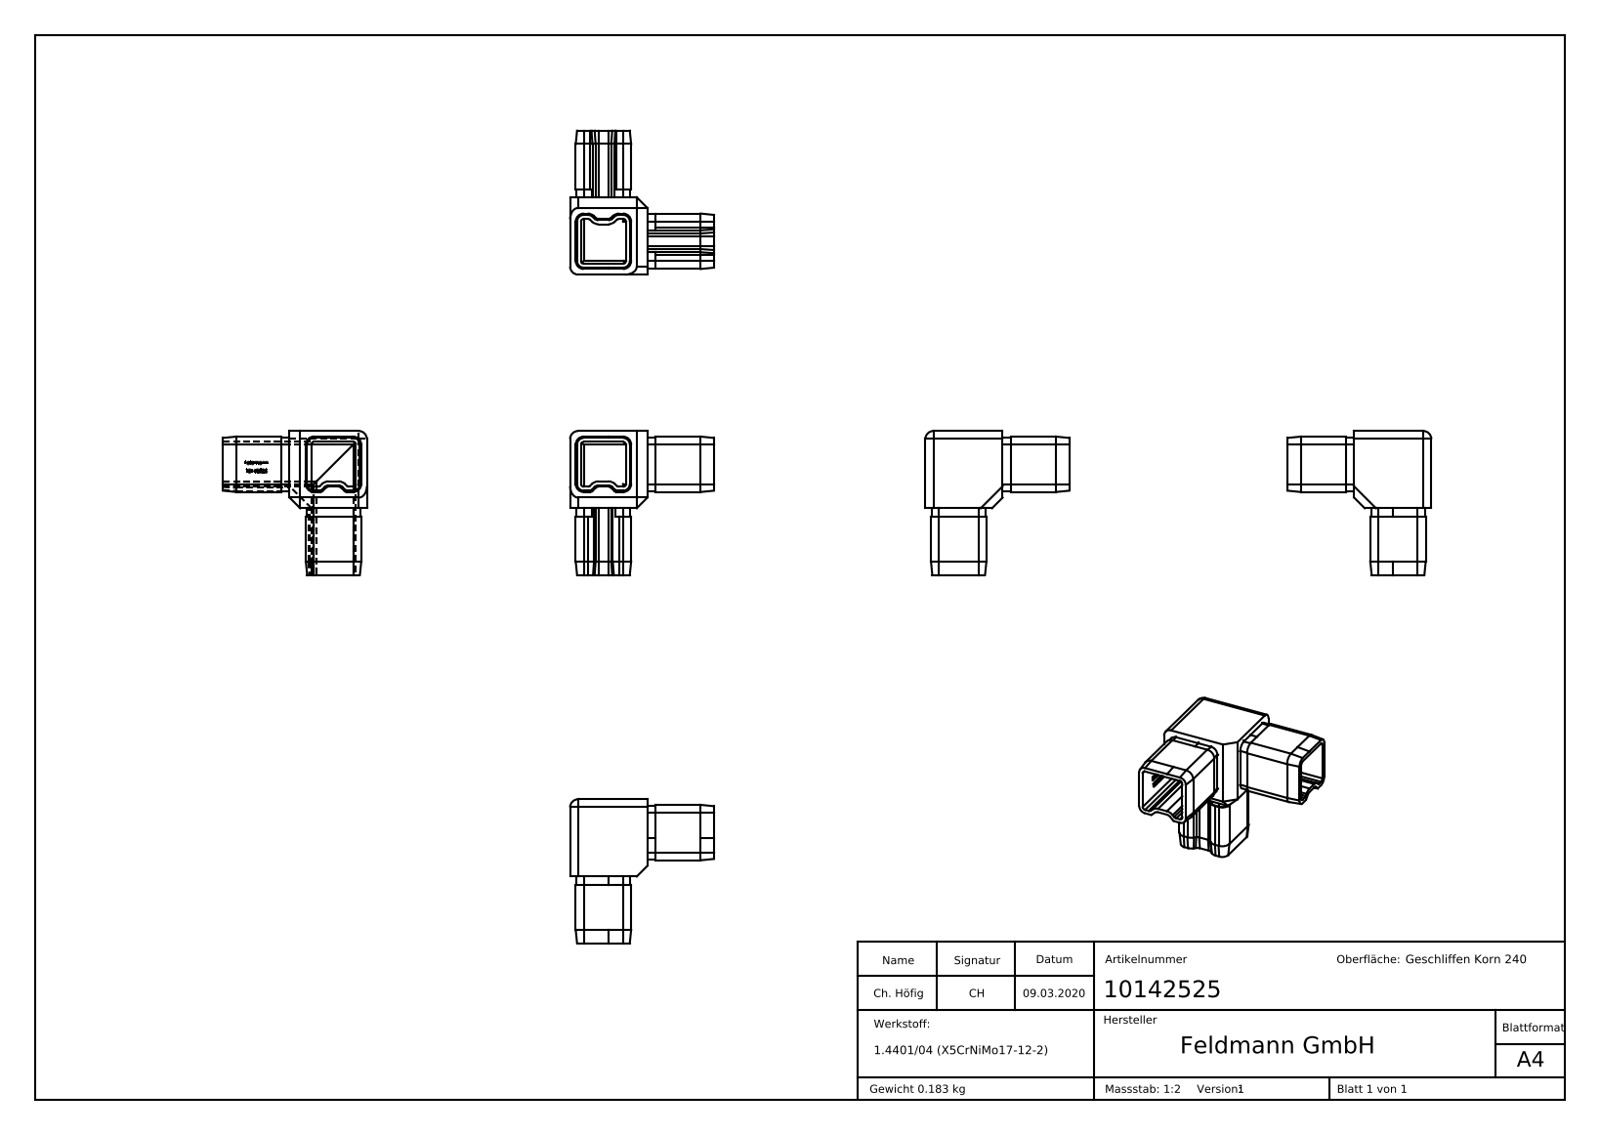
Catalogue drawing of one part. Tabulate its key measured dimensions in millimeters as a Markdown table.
| quantity | value |
| --- | --- |
| part name | 10142525 |
| STEP written by | SolidWorks 2015 (CONFIG_CONTROL_DESIGN) |
| units | millimeters |
| bodies | 1 solid, 434 faces (258 planar, 66 cylindrical, 110 other) |
| overall size | 54 × 54 × 54 |
| volume | 22 910 mm³ |
| surface area | 17 316 mm² |
| partial cylindrical surfaces (radius × count) | 3 × 17, 1 × 12, 2.7 × 12, 1.27 × 10, 1.5 × 6, 3.5 × 6, 3.27 × 2 |
| main face-to-face distances | 2, 16.8, 18.8, 4.1, 20.9, 2.1, 22.9, 20.8, 29, 26.9 |
